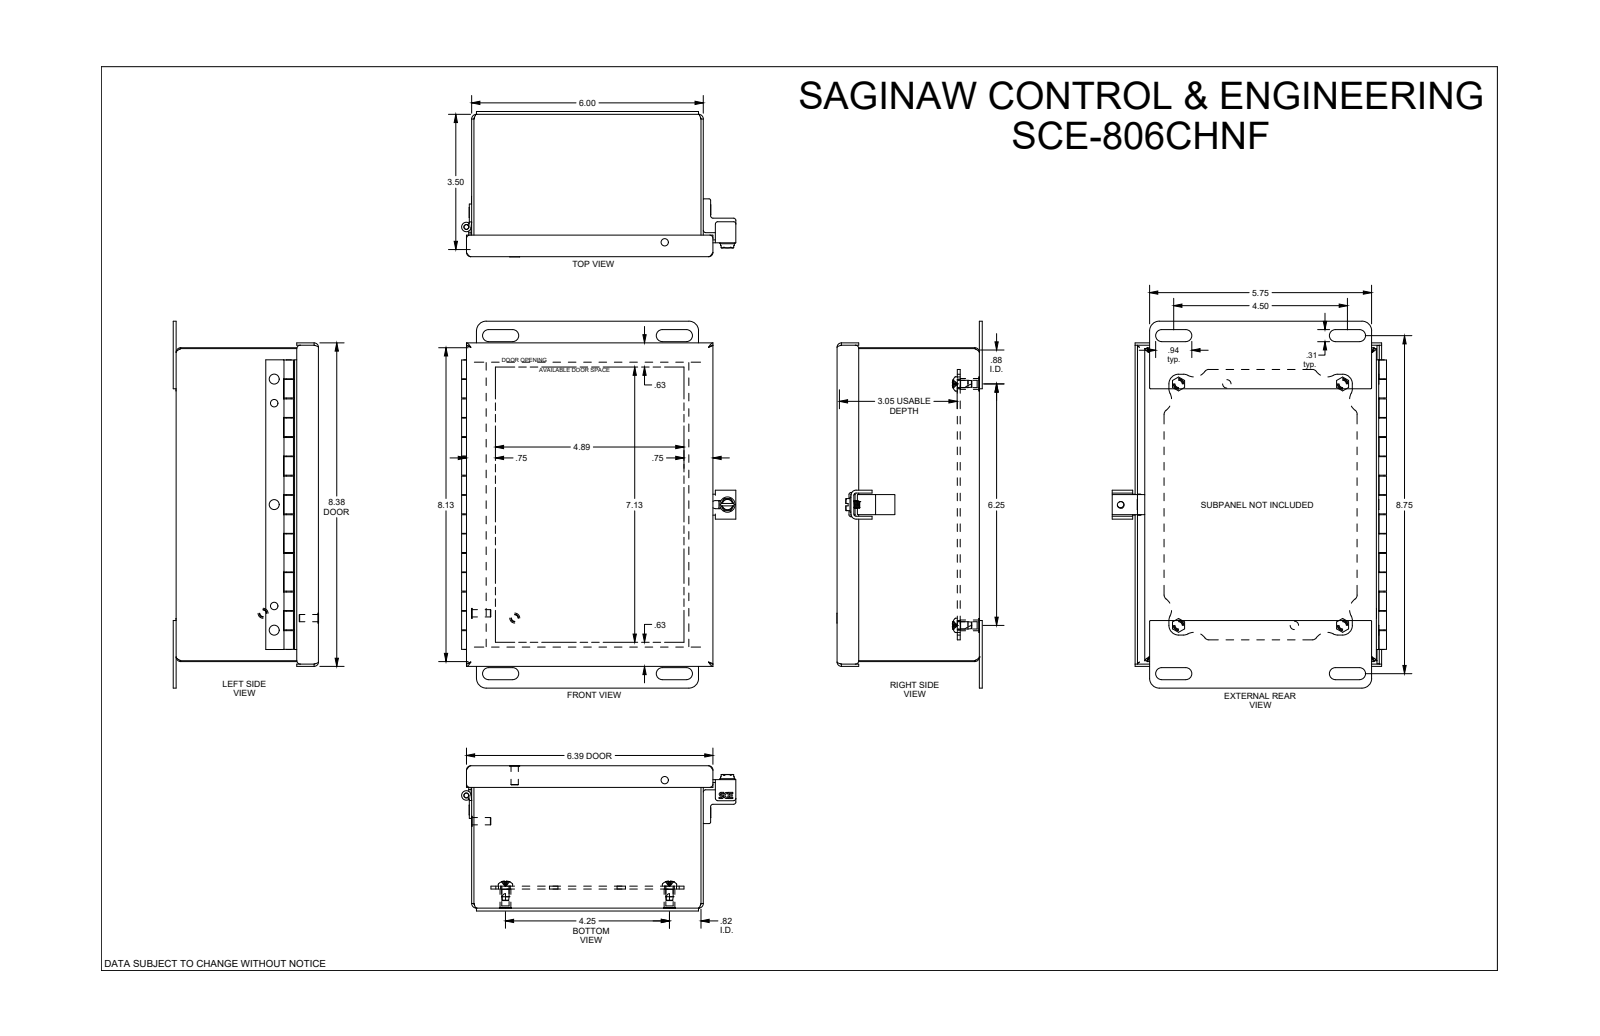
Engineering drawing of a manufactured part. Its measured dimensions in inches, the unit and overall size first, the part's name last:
Units: inches
Overall size (bounding box): 9.5 × 7.104 × 3.765
Round holes (diameter × count): ⌀0.19 ×8, ⌀0.193 ×6, ⌀0.25 ×4, ⌀0.281 ×4, ⌀0.193 ×2, ⌀0.218 ×2, ⌀0.126 ×1, ⌀0.156 ×1, ⌀0.187 ×1, ⌀0.266 ×1
Round bosses / shafts (diameter × count): ⌀0.188 ×11, ⌀0.256 ×6, ⌀0.373 ×4, ⌀0.28 ×4, ⌀0.396 ×1, ⌀0.246 ×1, ⌀0.123 ×1
Partial cylindrical surfaces — rounded edges, fillets, slot ends (radius × count): R0.01 ×56, R0.25 ×16, R0.06 ×13, R0.052 ×8, R0.112 ×8, R0.125 ×8, R0.156 ×8, R0.344 ×8
Main face-to-face distances: 0.06, 3.625, 5.94, 3.685, 3.565, 0.06, 0.075, 3.13, 0.57, 0.51
Hole centre spacings: 1.25, 3, 3.25, 3.251, 4.25, 6.25, 6.374, 6.933
Bodies: 0 solids, 1091 faces (500 planar, 293 cylindrical, 298 other)
Part name (STEP PRODUCT): SCE-806CHNF
STEP written by: SolidWorks 2019 (CONFIG_CONTROL_DESIGN)
